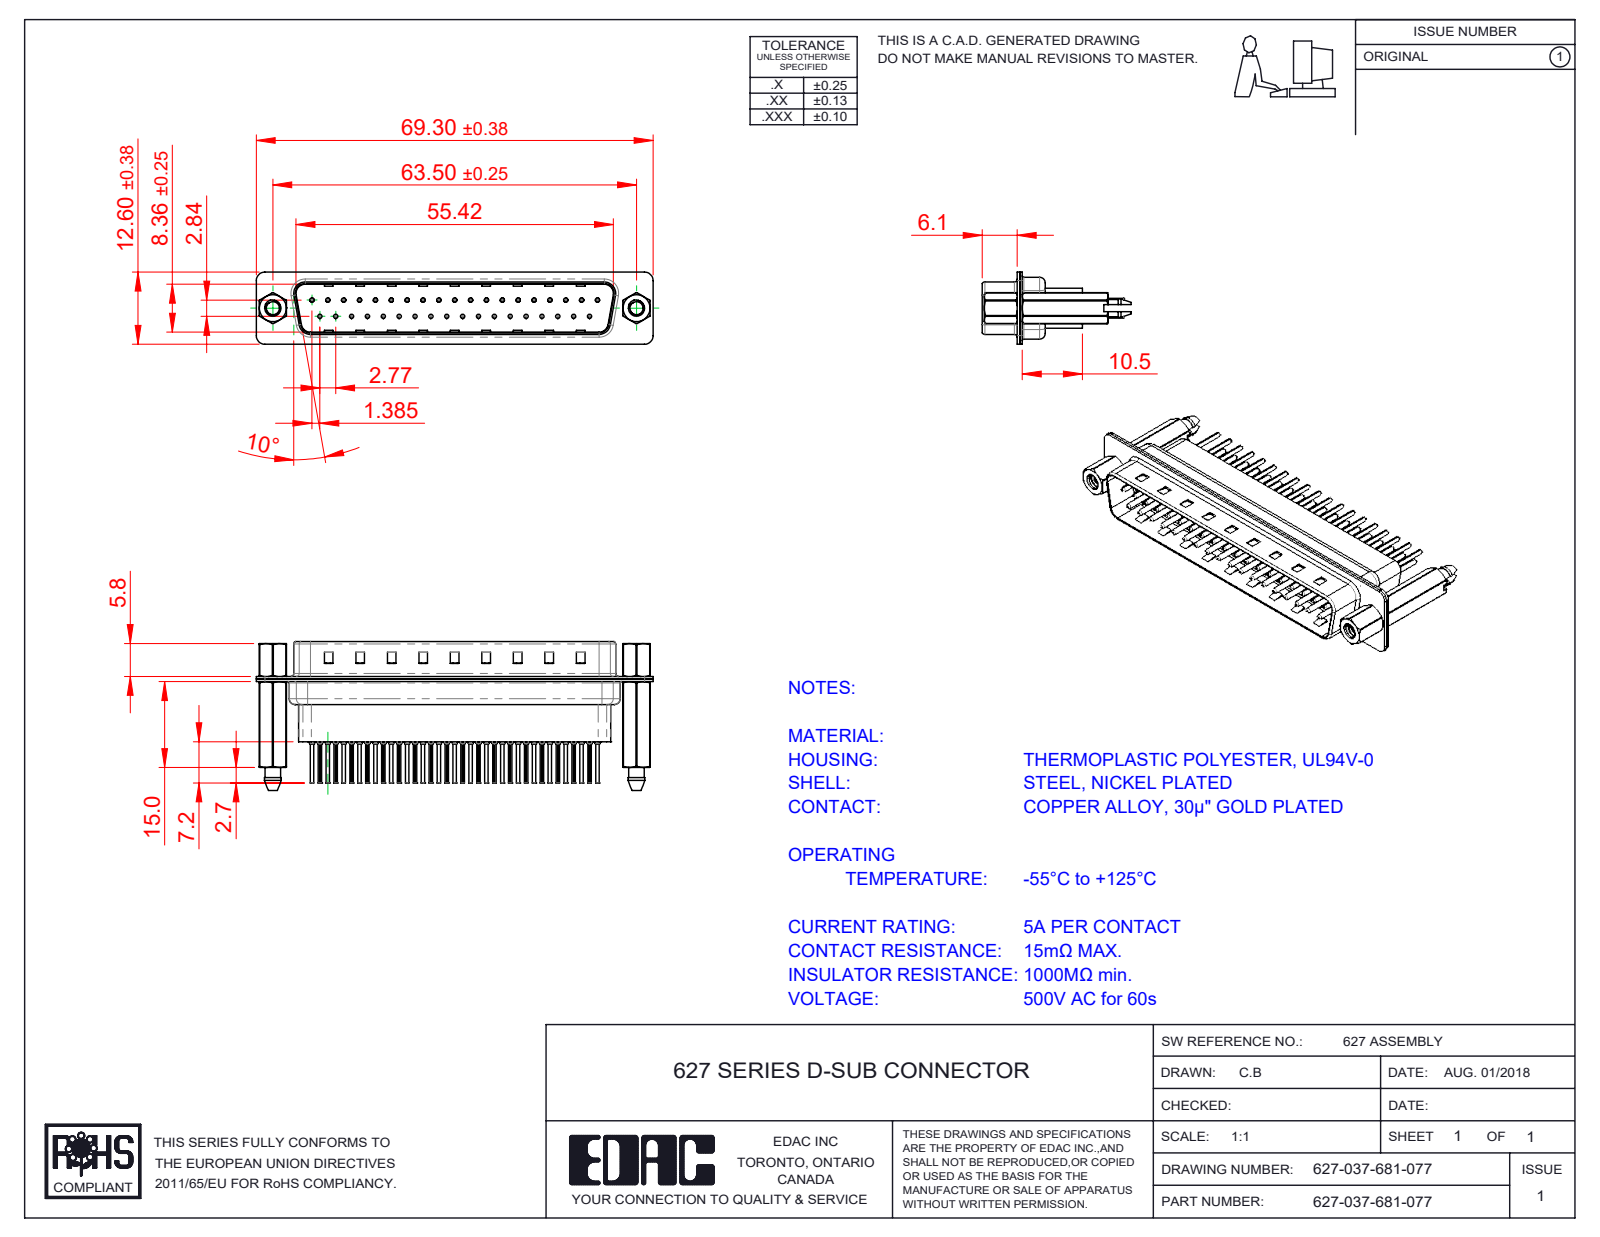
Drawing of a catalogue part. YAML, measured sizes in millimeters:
part_name: "627 4-40 Threaded Boardlock_HP81; 627 Housing_37 HP; 627 Contact Row 2_61; 627 Shell Front_37 Contacts (+4 more)"
step_written_by: "SolidWorks 2020 (CONFIG_CONTROL_DESIGN)"
units: millimeters
bodies: {solids: 44, faces: 4272, planar: 1145, cylindrical: 1648, other: 1479}
overall_size: [69.3, 25.9, 12.6]
volume: 5936
surface_area: 15227
round_holes:
  - {diameter: 0.2, count: 37}
  - {diameter: 0.35, count: 37}
  - {diameter: 1.1, count: 37}
  - {diameter: 1.6, count: 37}
  - {diameter: 2.26, count: 2}
  - {diameter: 2.29, count: 2}
  - {diameter: 4, count: 2}
  - {diameter: 4.8, count: 2}
round_bosses_or_shafts:
  - {diameter: 2, count: 37}
  - {diameter: 1.5, count: 37}
  - {diameter: 0.75, count: 37}
  - {diameter: 0.6, count: 37}
  - {diameter: 4.9, count: 2}
  - {diameter: 2.79, count: 2}
partial_cylinders:
  - {radius: 0.1, count: 74}
  - {radius: 1.5, count: 18}
  - {radius: 2, count: 12}
  - {radius: 1.6, count: 10}
  - {radius: 0.5, count: 8}
  - {radius: 0.25, count: 4}
  - {radius: 0.6, count: 4}
  - {radius: 0.65, count: 4}
face_to_face_distances: [0.4, 0.82, 9.58, 0.45, 0.68, 7.68, 1.5, 1.08, 8.08, 8.76]
hole_center_spacings: [3.16, 2.77, 5.54, 8.31, 5.04, 10.1, 11.08, 12.78]
